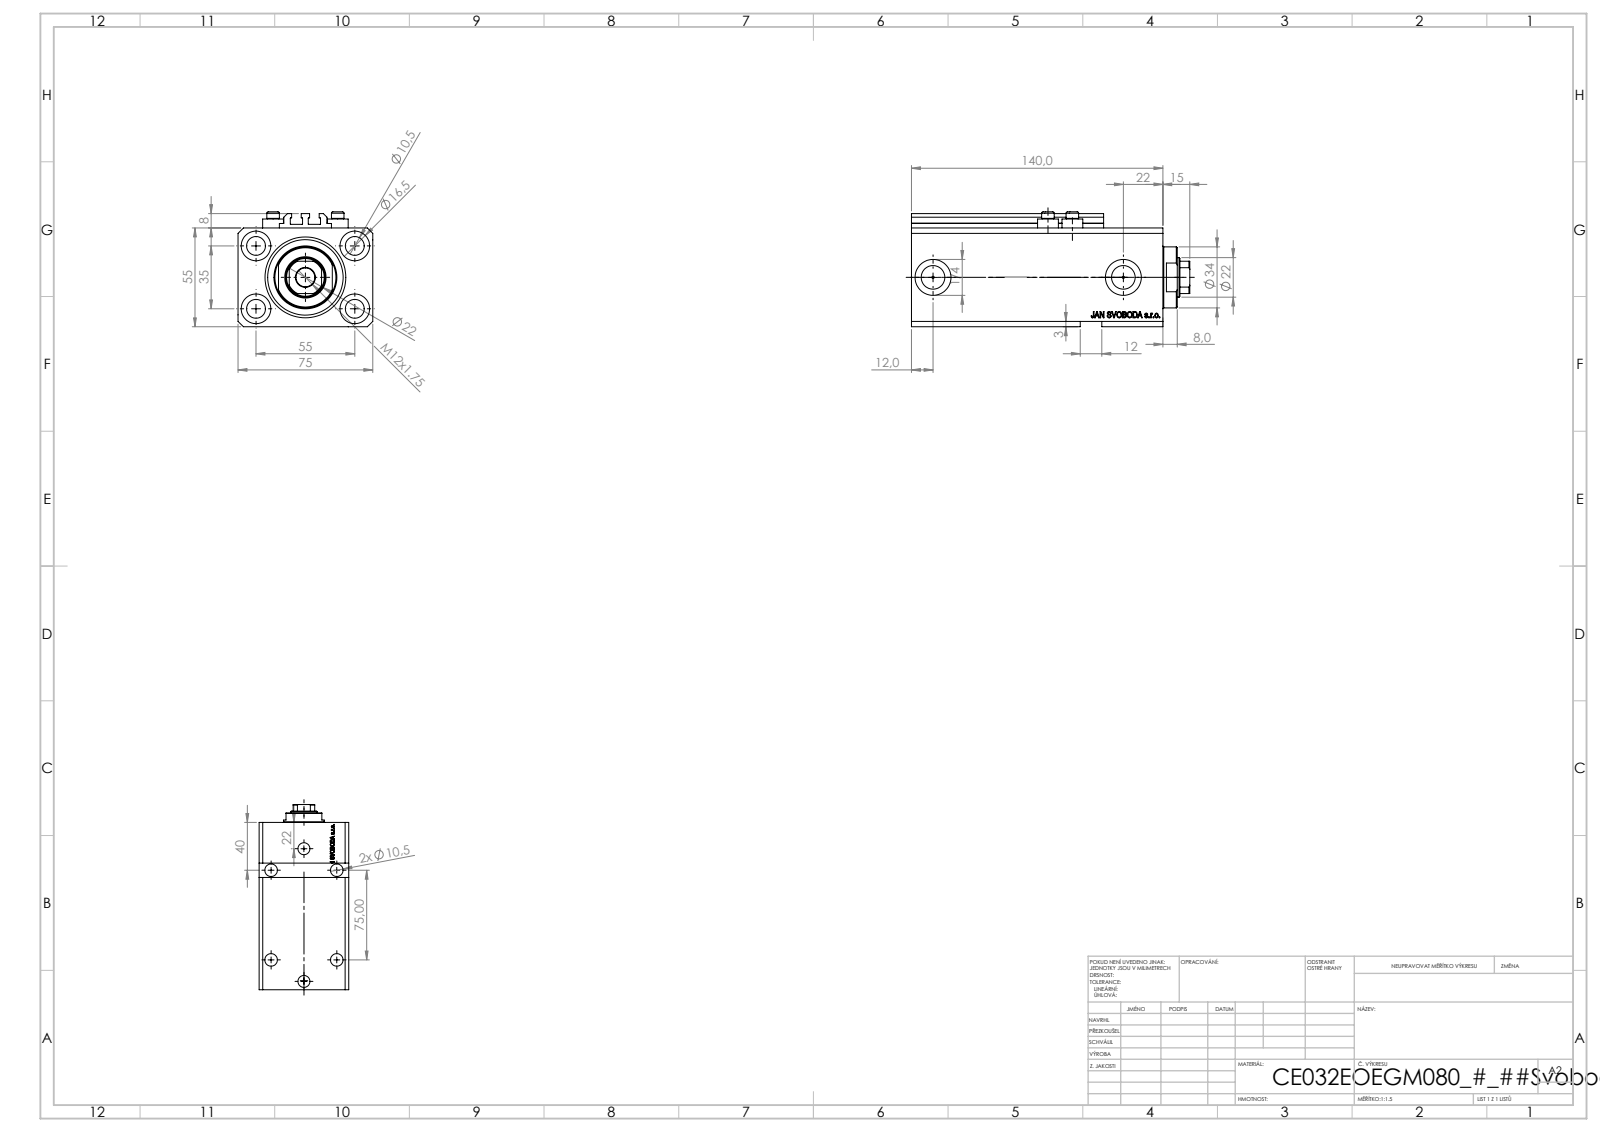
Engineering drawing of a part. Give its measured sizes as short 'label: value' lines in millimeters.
name: ALLEN BOLT V250CE; V250CE_VC_E; V250CE_E_Body; V250CE_C_VCP
written by: SolidWorks 2019 (CONFIG_CONTROL_DESIGN)
unit: mm
bodies: 8 solids, 1084 faces (514 planar, 146 cylindrical, 424 other)
size: 155 × 75 × 64
volume: 485 219 mm³; area: 115 303 mm²
holes: 9× ⌀10.5, 4× ⌀1.25, 4× ⌀4, 4× ⌀16.5, 2× ⌀10, 2× ⌀13.16, 2× ⌀20, 1× ⌀22, 1× ⌀32, 1× ⌀45
bosses: 4× ⌀11.6, 4× ⌀7, 1× ⌀34
rounds: 10× R0.2, 1× R10.5
face distances: 55, 75, 15, 140, 125, 3, 9.9, 57, 115.1, 130.1
hole spacings: 32.6, 32.87, 55, 96.98, 13.6, 14.09, 25.81, 32.58
